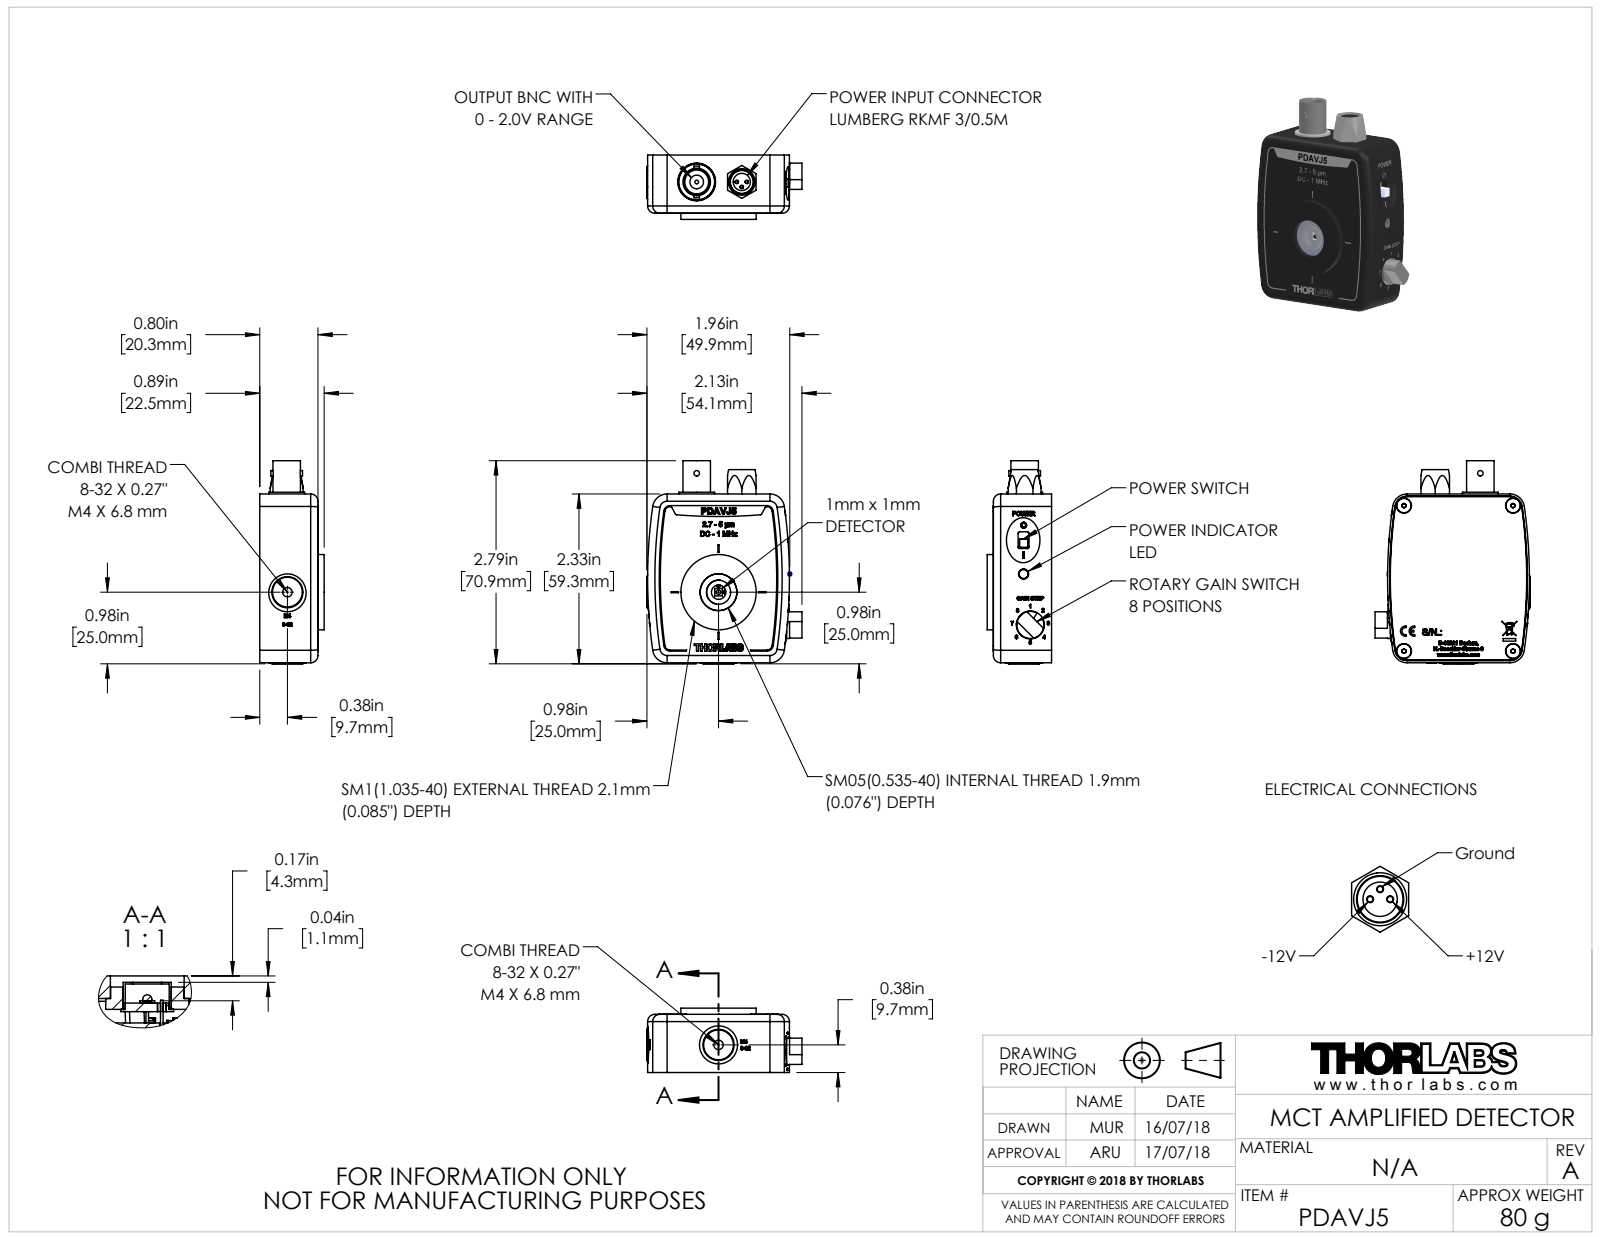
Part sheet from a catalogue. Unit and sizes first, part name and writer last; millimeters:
Units: millimetres
Overall size (bounding box): 70.9 × 54.13 × 22.48
Round holes (diameter × count): ⌀1.78 ×7, ⌀1 ×3, ⌀0.45 ×2, ⌀1.5 ×2, ⌀3.3 ×2, ⌀0.38 ×1, ⌀0.89 ×1, ⌀1.27 ×1, ⌀2.92 ×1, ⌀3.56 ×1, ⌀3.81 ×1, ⌀5 ×1
Round bosses / shafts (diameter × count): ⌀5 ×4, ⌀2.18 ×4, ⌀26.29 ×1, ⌀14.5 ×1, ⌀12.8 ×1, ⌀12.5 ×1, ⌀9.6 ×1, ⌀9.47 ×1
Partial cylindrical surfaces — rounded edges, fillets, slot ends (radius × count): R0.51 ×18, R0.76 ×8, R2.54 ×8, R0.56 ×4, R1.6 ×4, R1.85 ×4, R2.23 ×4, R4.06 ×4
Main face-to-face distances: 1.5, 16.94, 18.44, 1.78, 18.72, 20.22, 58.93, 3.94, 2.16, 20.88
Hole centre spacings: 1.75, 2.47, 2.54, 19.81, 22.18, 28.04, 29.95, 33.61
Volume: 22 345 mm³ · Surface area: 23 440 mm²
Bodies: 72 solids, 2523 faces (1242 planar, 307 cylindrical, 974 other)
Part name (STEP PRODUCT): M0096-10-0509_PDAVJ5
STEP written by: SolidWorks 2018 (CONFIG_CONTROL_DESIGN)
